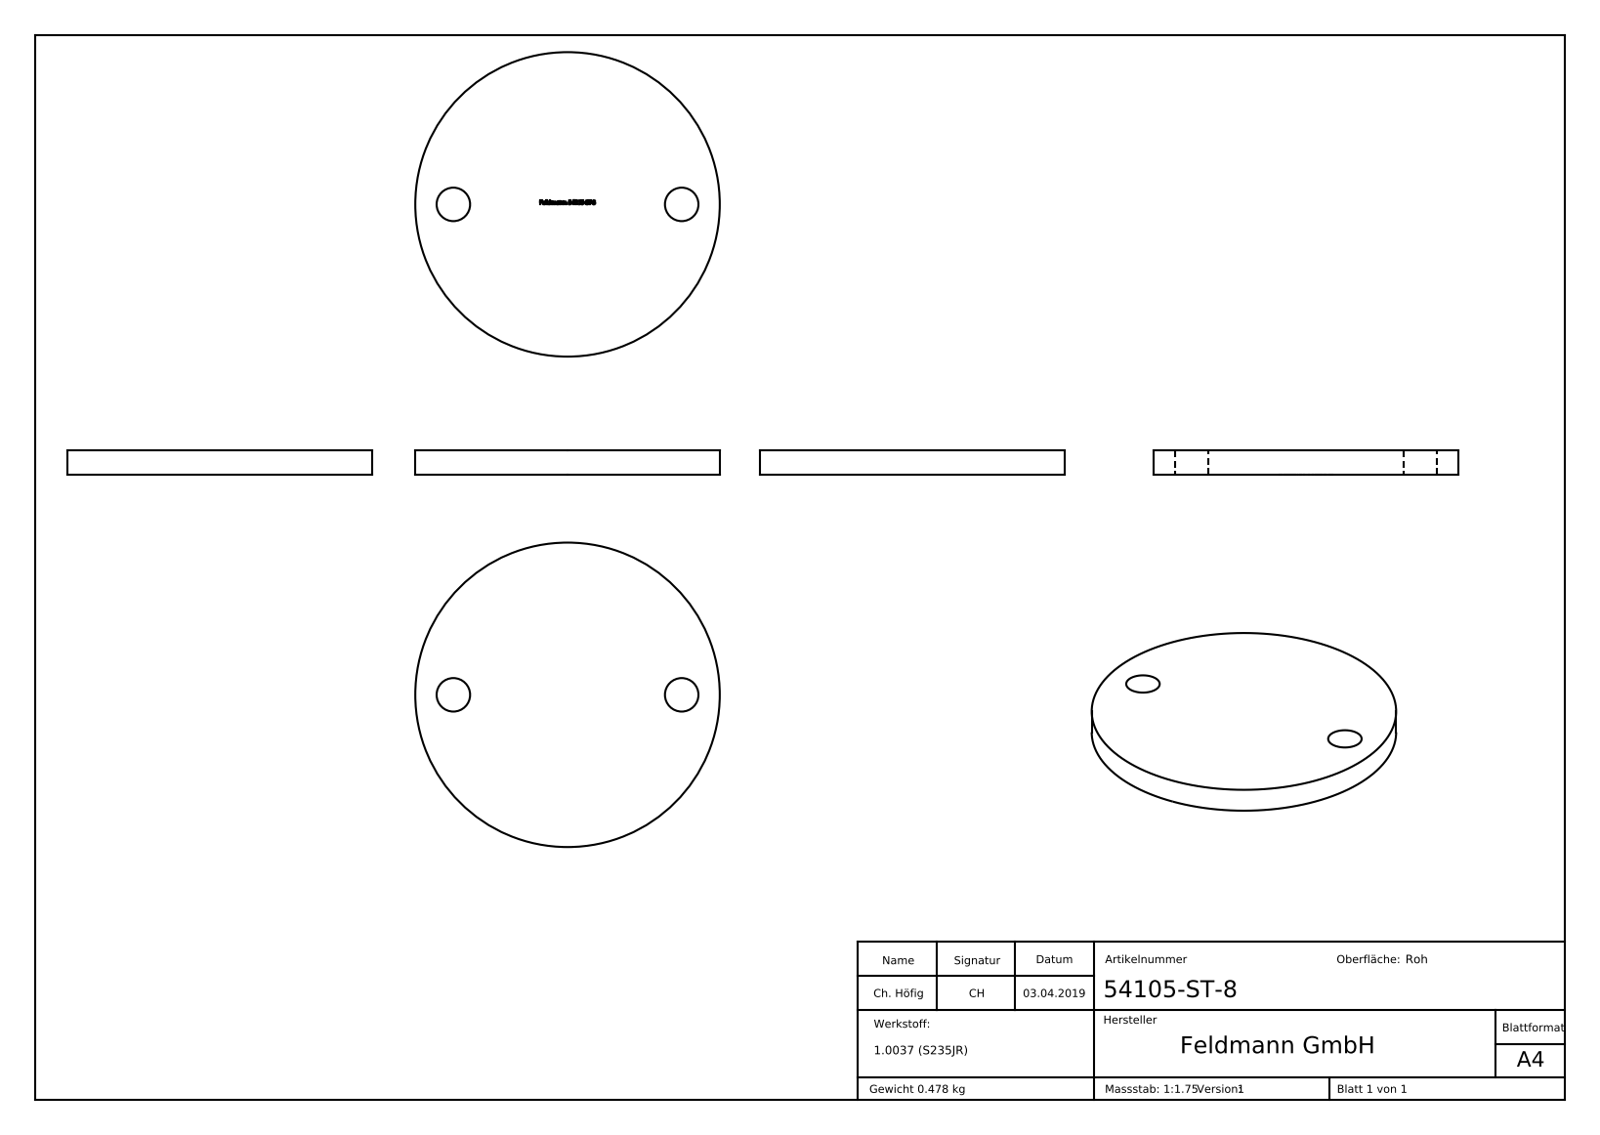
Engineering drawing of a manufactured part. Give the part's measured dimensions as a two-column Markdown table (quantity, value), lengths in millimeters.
| quantity | value |
| --- | --- |
| part name | 54105-ST-8 |
| STEP written by | SolidWorks 2015 (CONFIG_CONTROL_DESIGN) |
| units | millimeters |
| bodies | 1 solid, 241 faces (130 planar, 6 cylindrical, 105 other) |
| overall size | 100 × 100 × 8 |
| volume | 61 311 mm³ |
| surface area | 18 403 mm² |
| round holes (diameter × count) | 11 × 2 |
| round bosses / shafts (diameter × count) | 100 × 1 |
| main face-to-face distances | 8, 7.9, 5.22, 4.31, 0.39, 2.97, 2.02, 14.14, 0.88, 16.16 |
| hole center spacings | 75 |
